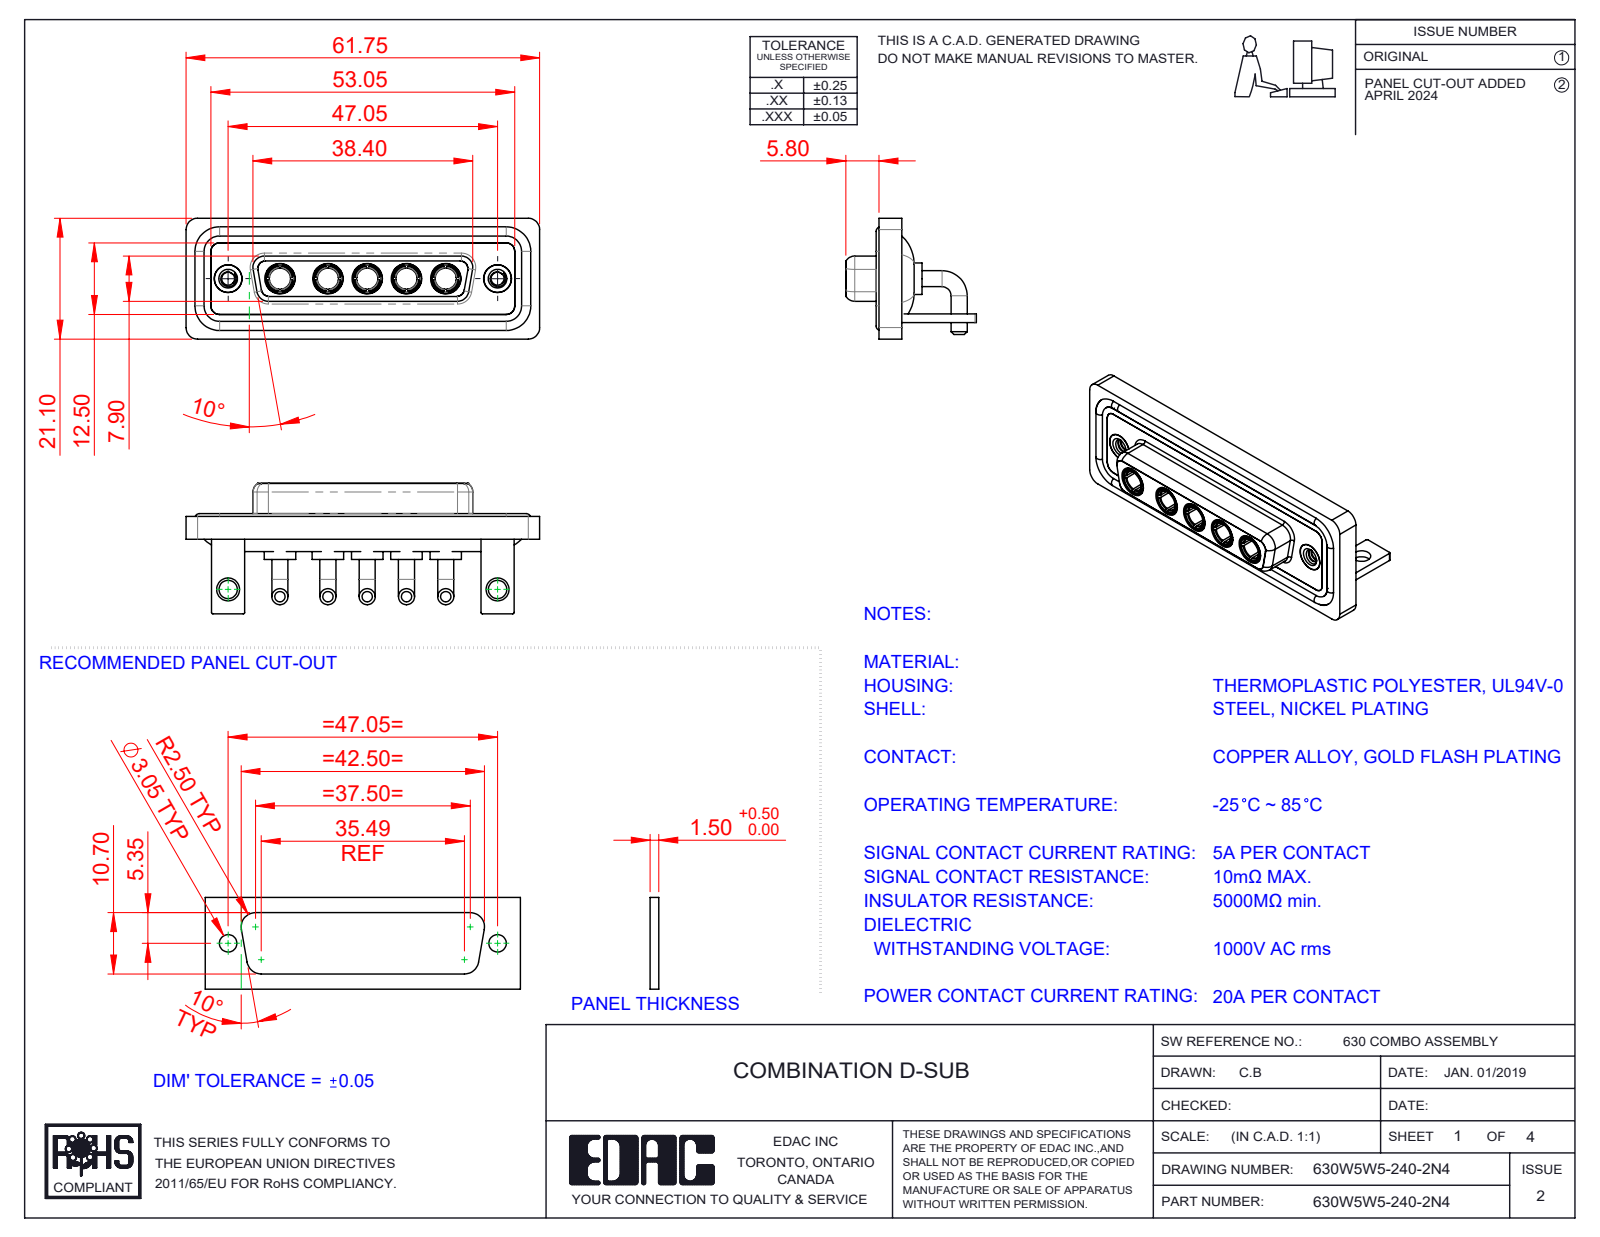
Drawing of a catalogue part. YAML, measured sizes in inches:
part_name: "630Combo Threaded Rivet_2; 630Combo Waterproof Housing_25 Contacts; Power Socket_20A RA; 630Combo Shell Rear_25 Contacts (+4 more)"
step_written_by: "SolidWorks 2023 (CONFIG_CONTROL_DESIGN)"
units: inches
bodies: {solids: 19, faces: 824, planar: 270, cylindrical: 337, other: 217}
overall_size: [2.431, 0.898, 0.831]
volume: 0.537
surface_area: 22.55
round_holes:
  - {diameter: 0.191, count: 7}
  - {diameter: 0.146, count: 5}
  - {diameter: 0.209, count: 5}
  - {diameter: 0.089, count: 2}
  - {diameter: 0.126, count: 2}
  - {diameter: 0.157, count: 2}
  - {diameter: 0.159, count: 2}
  - {diameter: 0.197, count: 2}
round_bosses_or_shafts:
  - {diameter: 0.11, count: 10}
  - {diameter: 0.217, count: 5}
  - {diameter: 0.205, count: 5}
  - {diameter: 0.195, count: 5}
  - {diameter: 0.187, count: 5}
  - {diameter: 0.148, count: 5}
  - {diameter: 0.063, count: 4}
  - {diameter: 0.195, count: 2}
partial_cylinders:
  - {radius: 0.079, count: 19}
  - {radius: 0.059, count: 18}
  - {radius: 0.01, count: 16}
  - {radius: 0.053, count: 8}
  - {radius: 0.063, count: 8}
  - {radius: 0.02, count: 5}
  - {radius: 0.083, count: 5}
  - {radius: 0.024, count: 4}
face_to_face_distances: [0.016, 0.071, 0.114, 0.146, 0.059, 0.161, 0.043, 0.055, 0.063, 0.098]
hole_center_spacings: [0.27, 0.356, 1.496, 1.852, 0.27, 0.33, 0.54, 0.541]
